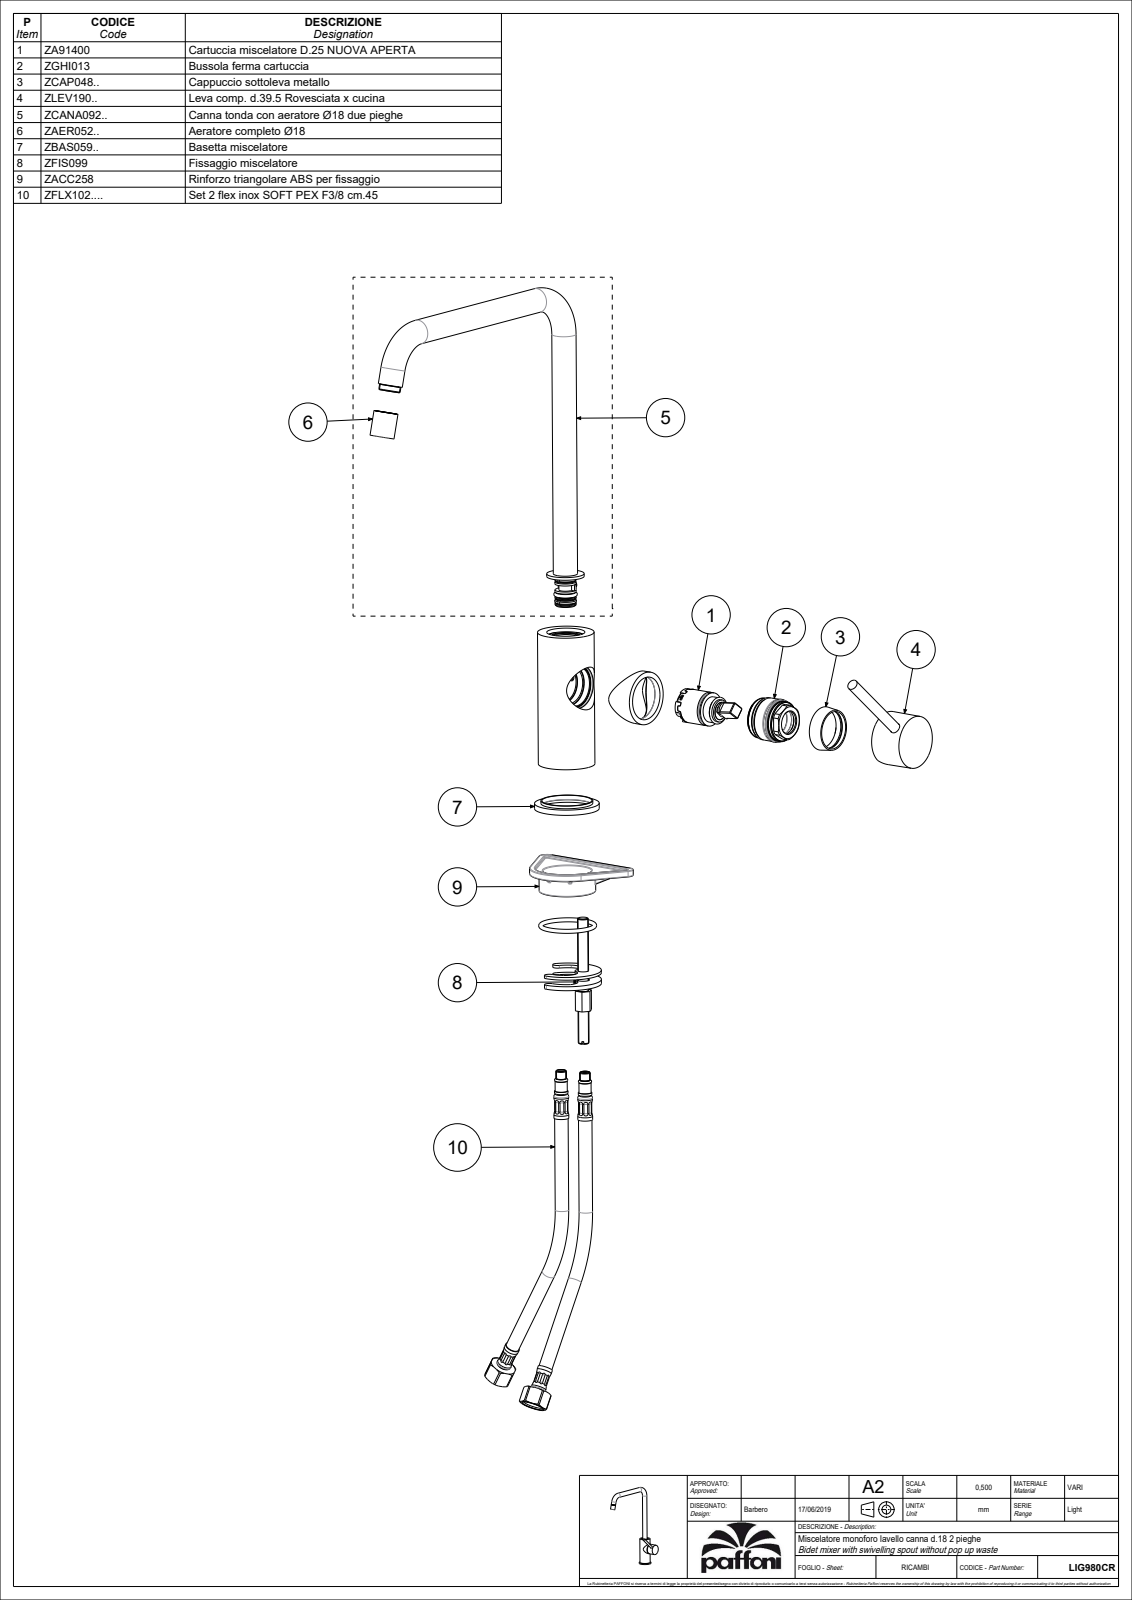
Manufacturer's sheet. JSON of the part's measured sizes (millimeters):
{"part_name": "1000497GR; 4071653_CORPO; 4071653_ROTAZIONE; 4071653_PERNO (+8 more)", "step_written_by": "CREO PARAMETRIC BY PTC INC, 2020044 (CONFIG_CONTROL_DESIGN)", "units": "millimeters", "bodies": {"solids": 31, "faces": 1763, "planar": 457, "cylindrical": 790, "other": 516}, "overall_size": [325.5, 240.45, 79.15], "volume_mm3": 193681, "surface_area_mm2": 117191, "round_holes": [[0.5, 51], [5, 4], [6, 4], [14, 4], [4, 3], [3.2, 2], [6.5, 2], [7, 2], [8, 2], [8.6, 2], [9.2, 2], [11, 2]], "round_bosses_or_shafts": [[18, 3], [15, 2], [13, 2], [8, 2], [3, 2], [48, 1], [42, 1], [39.5, 1]], "partial_cylinders_radius": [[0.5, 68], [0.3, 34], [1, 22], [3, 12], [0.7, 10], [0.25, 8], [0.8, 6], [3.5, 5]], "face_to_face_distances": [3, 2, 0.5, 2.5, 1, 7, 96.5, 3.5, 97, 100], "hole_center_spacings": [1.5, 3.35, 2.12, 4.74, 3, 5.41, 4.24, 4.5]}
